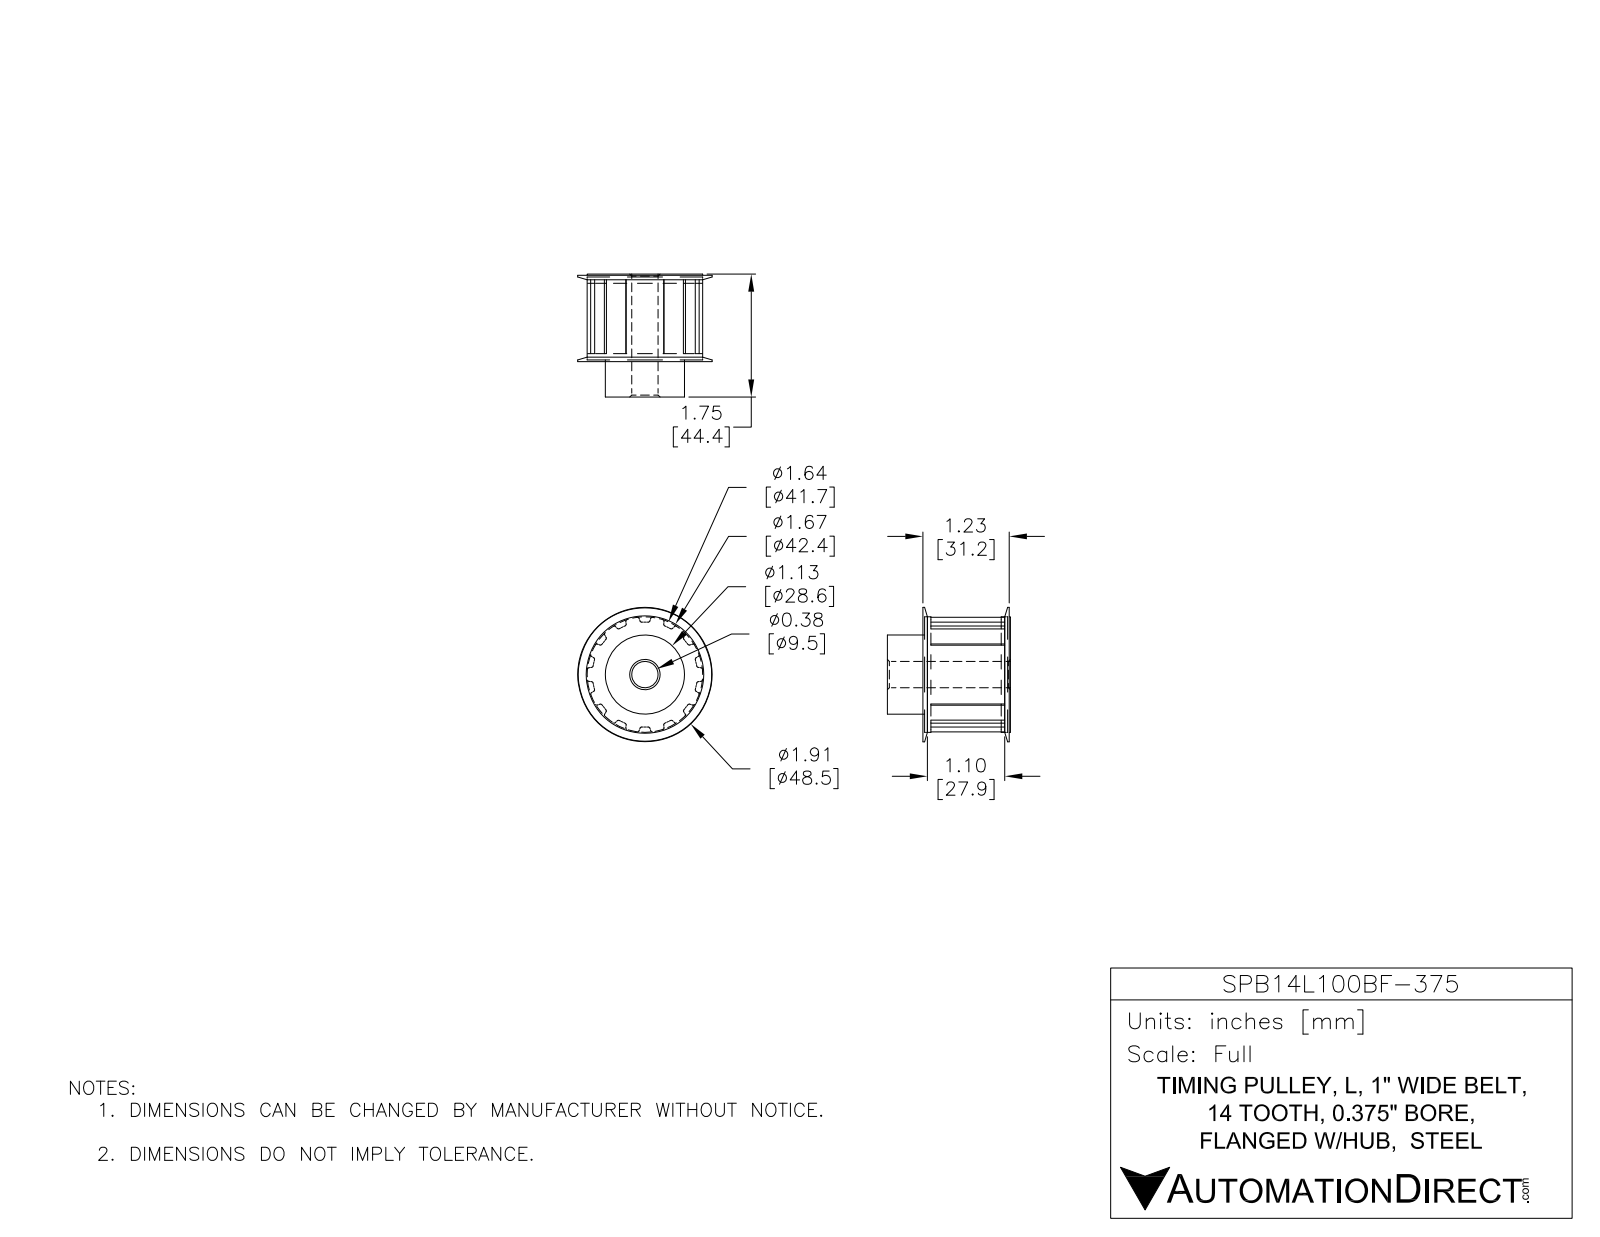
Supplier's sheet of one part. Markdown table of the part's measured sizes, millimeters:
| quantity | value |
| --- | --- |
| part name | SPB14L100BF-375 |
| STEP written by | SolidWorks 2017 (AUTOMOTIVE_DESIGN) |
| units | millimeters |
| bodies | 1 solid, 155 faces (48 planar, 89 cylindrical, 18 other) |
| overall size | 48.4 × 48.4 × 43.9 |
| volume | 47 340 mm³ |
| surface area | 11 860 mm² |
| round holes (diameter × count) | 9.5 × 1 |
| round bosses / shafts (diameter × count) | 31.8 × 1 |
| partial cylindrical surfaces (radius × count) | 0.4 × 56, 19.5 × 1 |
| main face-to-face distances | 1, 41.7, 43.9, 31, 12.9, 30, 42.9, 12.9, 2, 29 |
